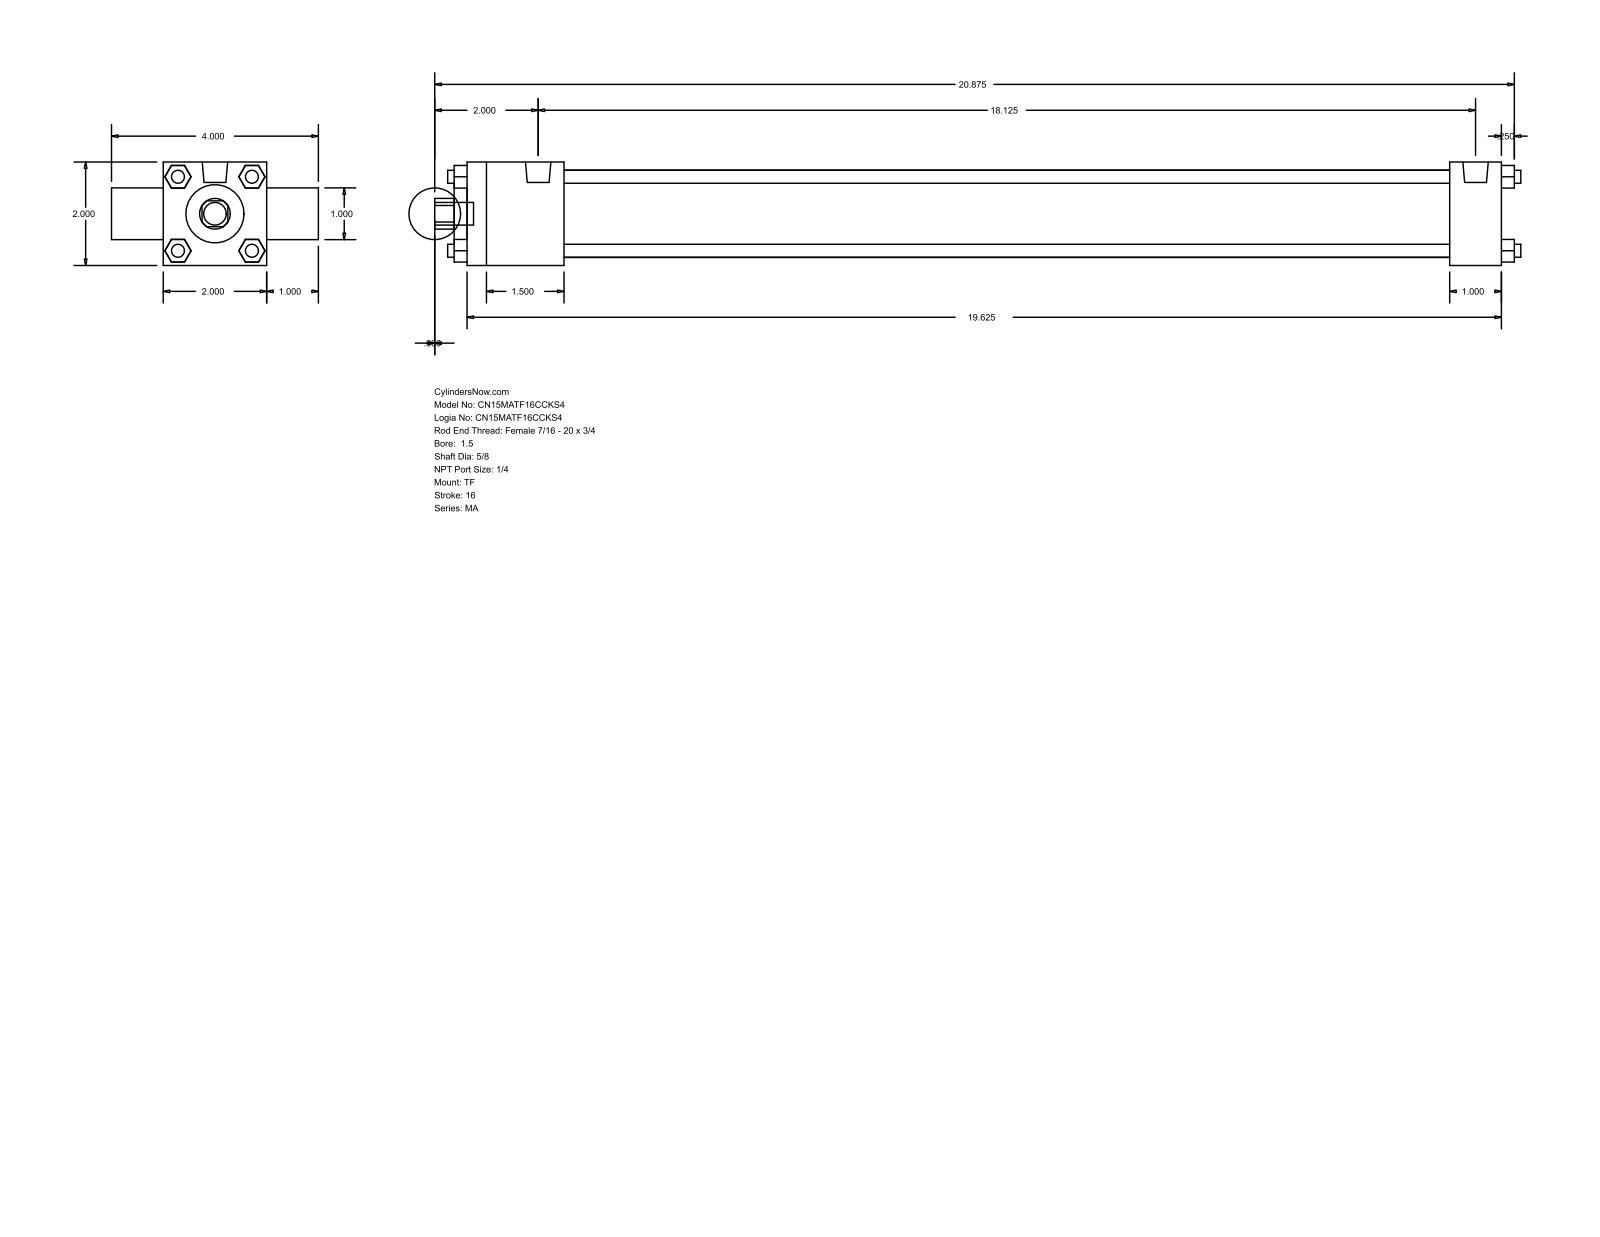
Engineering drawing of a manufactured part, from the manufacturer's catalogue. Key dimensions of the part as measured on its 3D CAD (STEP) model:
Part name (STEP PRODUCT): MA_TF__0150_0.625
STEP written by: GSSL Pune (CONFIG_CONTROL_DESIGN)
Units: millimetres
Bodies: 0 solids, 120 faces (92 planar, 28 cylindrical, 0 other)
Overall size (bounding box): 533.4 × 101.6 × 50.8
Round holes (diameter × count): ⌀15.88 ×1, ⌀25.4 ×1, ⌀28.57 ×1, ⌀42.93 ×1
Round bosses / shafts (diameter × count): ⌀6.35 ×4, ⌀7.94 ×3, ⌀12.49 ×2, ⌀11.11 ×1
Partial cylindrical surfaces — rounded edges, fillets, slot ends (radius × count): R7.54 ×1
Main face-to-face distances: 50.8, 25.4, 508, 514.35, 6.35, 76.2, 47.62, 482.6, 434.98, 460.38
